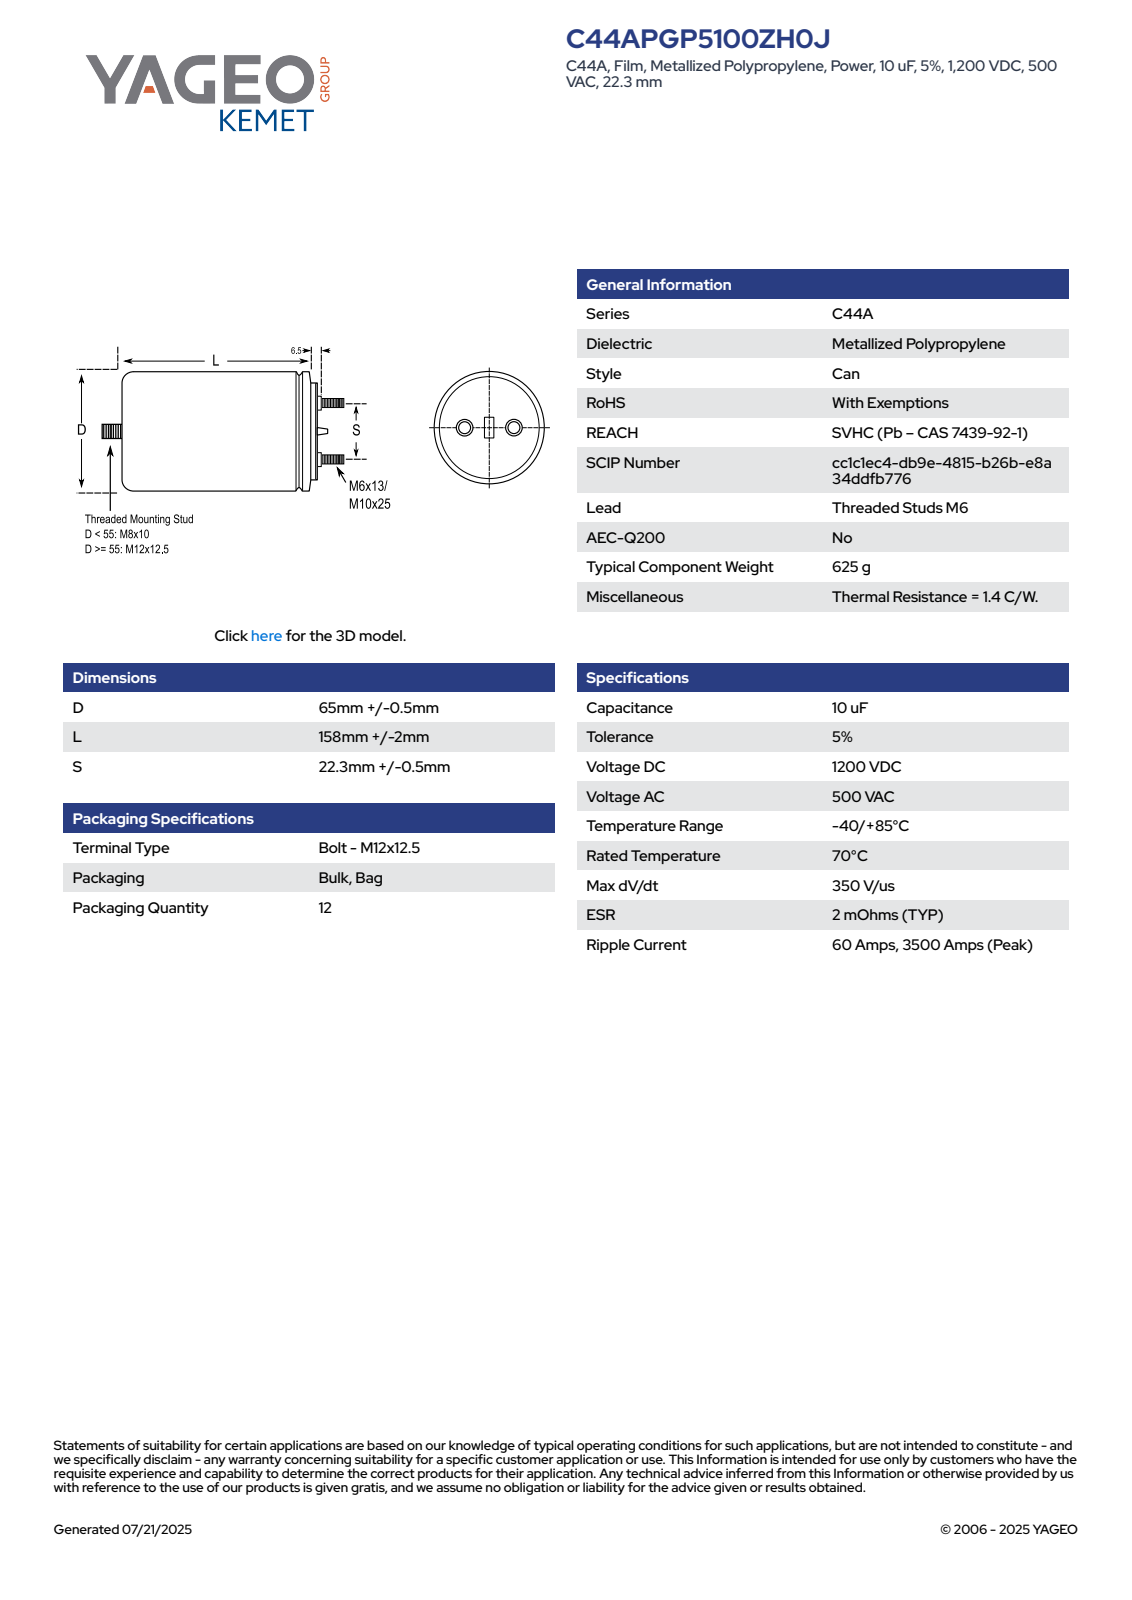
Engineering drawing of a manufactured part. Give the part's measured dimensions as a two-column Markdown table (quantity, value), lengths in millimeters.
| quantity | value |
| --- | --- |
| part name | CFP_C44A_65X158_D65.5L160S22.3 |
| STEP written by | SolidWorks 2014 (AUTOMOTIVE_DESIGN) |
| units | millimeters |
| bodies | 1 solid, 102 faces (29 planar, 34 cylindrical, 39 other) |
| overall size | 192 × 65.5 × 65.5 |
| volume | 547 296 mm³ |
| surface area | 40 956 mm² |
| round bosses / shafts (diameter × count) | 9 × 2, 6 × 2, 65.5 × 1, 51.37 × 1, 12 × 1 |
| partial cylindrical surfaces (radius × count) | 32.74 × 1 |
| main face-to-face distances | 165, 12.5, 177.5, 179, 166.5, 1.5, 192, 179.5, 14.5, 13 |
